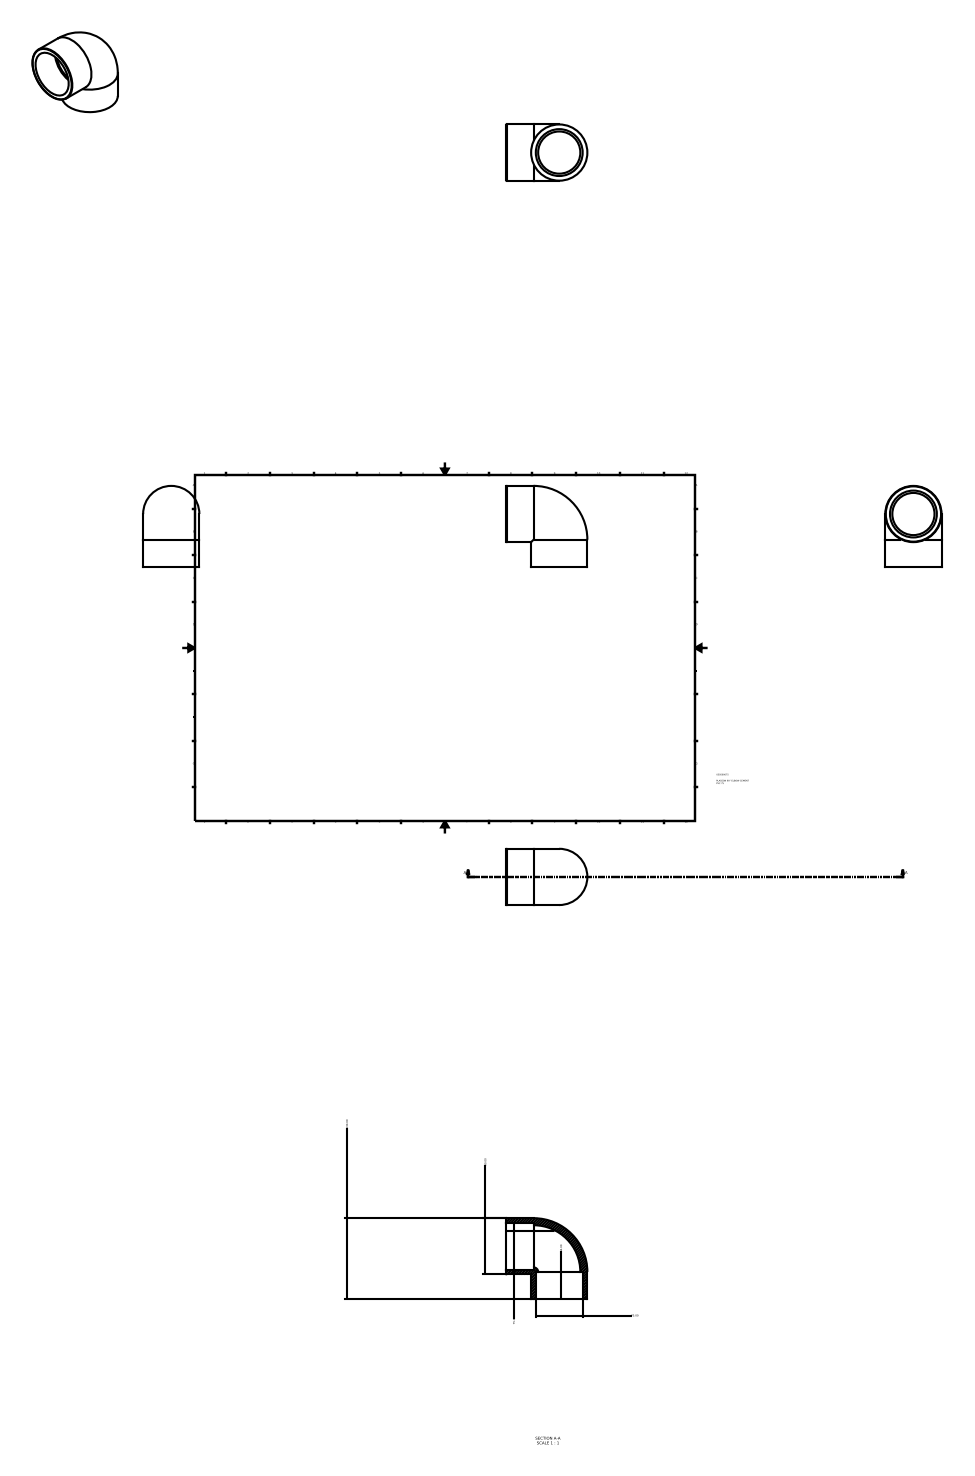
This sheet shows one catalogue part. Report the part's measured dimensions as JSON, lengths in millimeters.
{"part_name": "050500075", "step_written_by": "Autodesk Inventor 2015 (AUTOMOTIVE_DESIGN)", "units": "millimeters", "bodies": {"solids": 1, "faces": 11, "planar": 4, "cylindrical": 4, "other": 3}, "overall_size": [130, 130, 90], "volume_mm3": 354824, "surface_area_mm2": 82949, "round_holes": [[75, 2]], "round_bosses_or_shafts": [[90, 2]], "face_to_face_distances": [44]}
